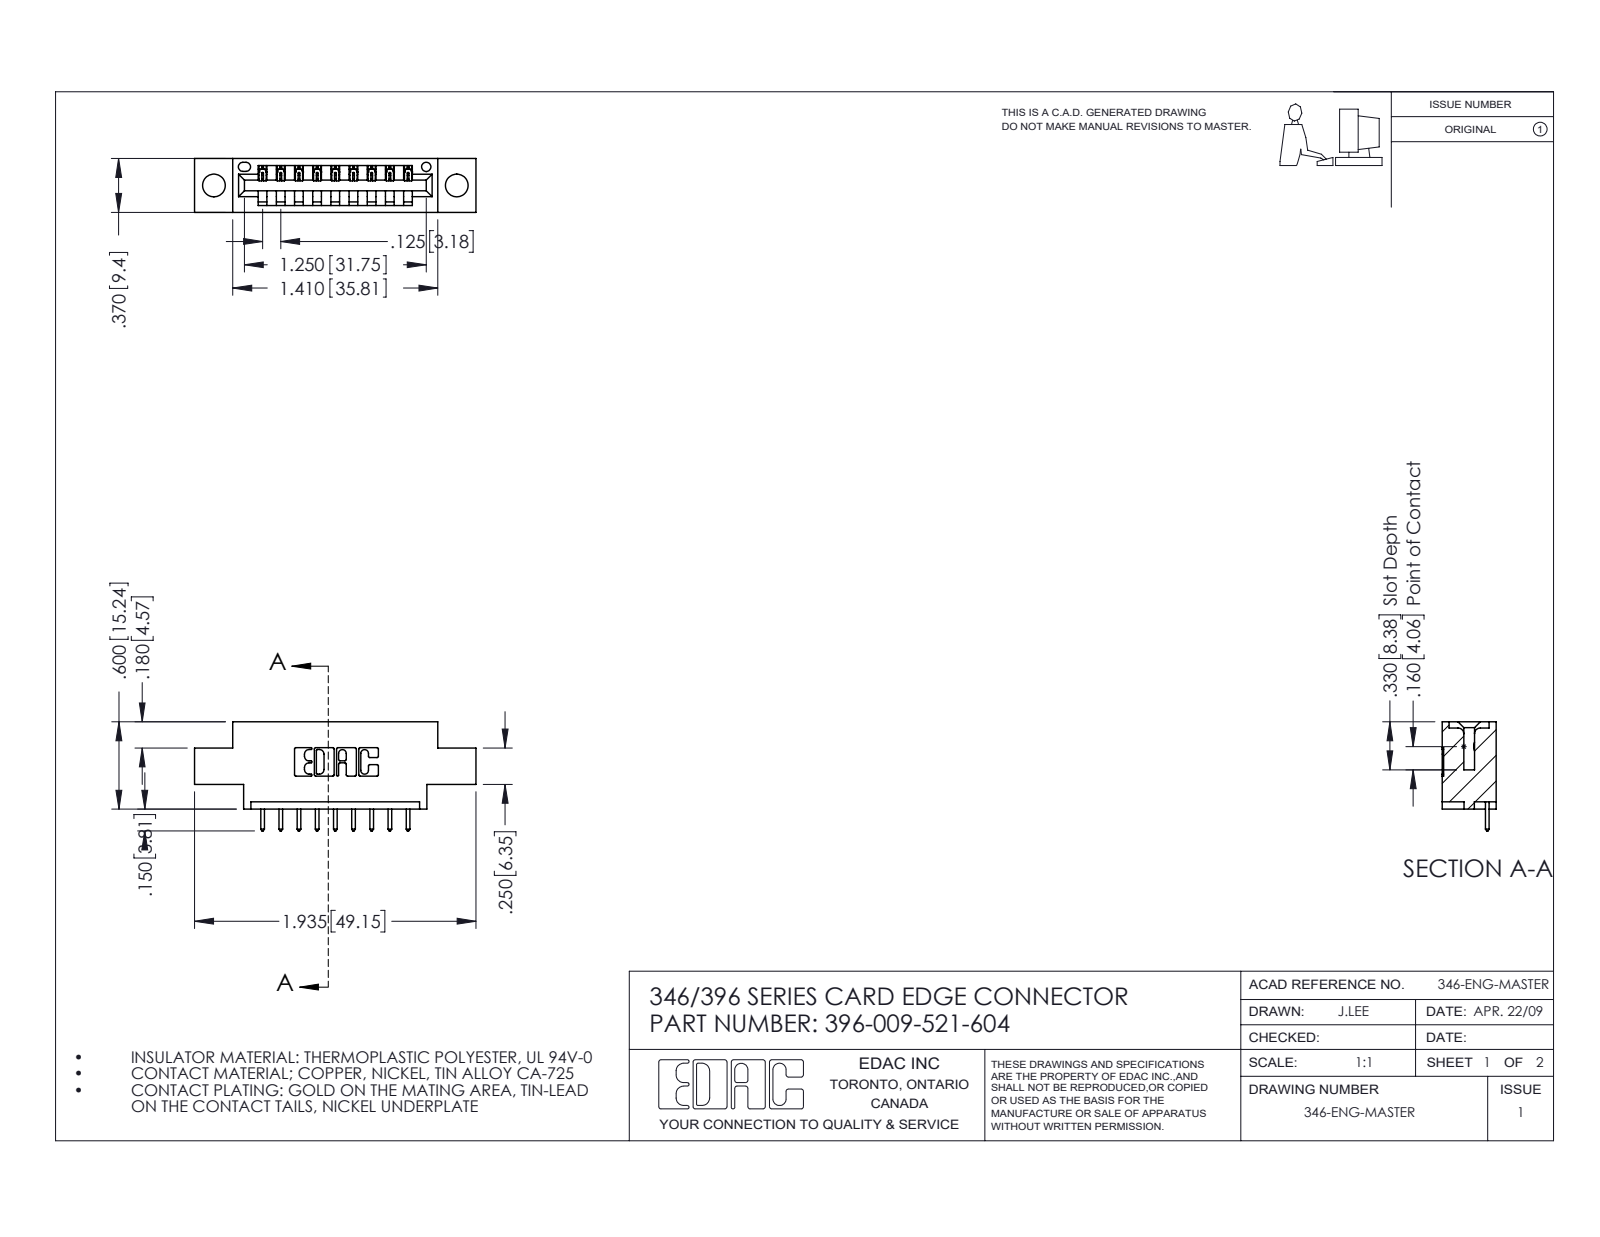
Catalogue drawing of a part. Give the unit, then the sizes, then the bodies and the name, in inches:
Units: inches
Overall size (bounding box): 1.935 × 0.75 × 0.37
Round holes (diameter × count): ⌀0.156 ×2, ⌀0.064 ×1
Partial cylindrical surfaces — rounded edges, fillets, slot ends (radius × count): R0.01 ×22, R0.006 ×18, R0.01 ×18, R0.007 ×6, R0.031 ×6, R0.026 ×3, R0.031 ×2, R0.04 ×2
Main face-to-face distances: 0.25, 0.37, 0.048, 0.322, 0.148, 0.222, 0.1, 0.174, 0.072, 0.298
Hole centre spacings: 0.246, 1.465, 1.67
Volume: 0.257 in³ · Surface area: 7.391 in²
Bodies: 10 solids, 648 faces (440 planar, 208 cylindrical, 0 other)
Part name (STEP PRODUCT): 396-009-521-604; 345-292-001_345-293-121; 346 Part_0.170 Offset - 0.156 Dia-TH
STEP written by: SolidWorks 2016 (CONFIG_CONTROL_DESIGN)
